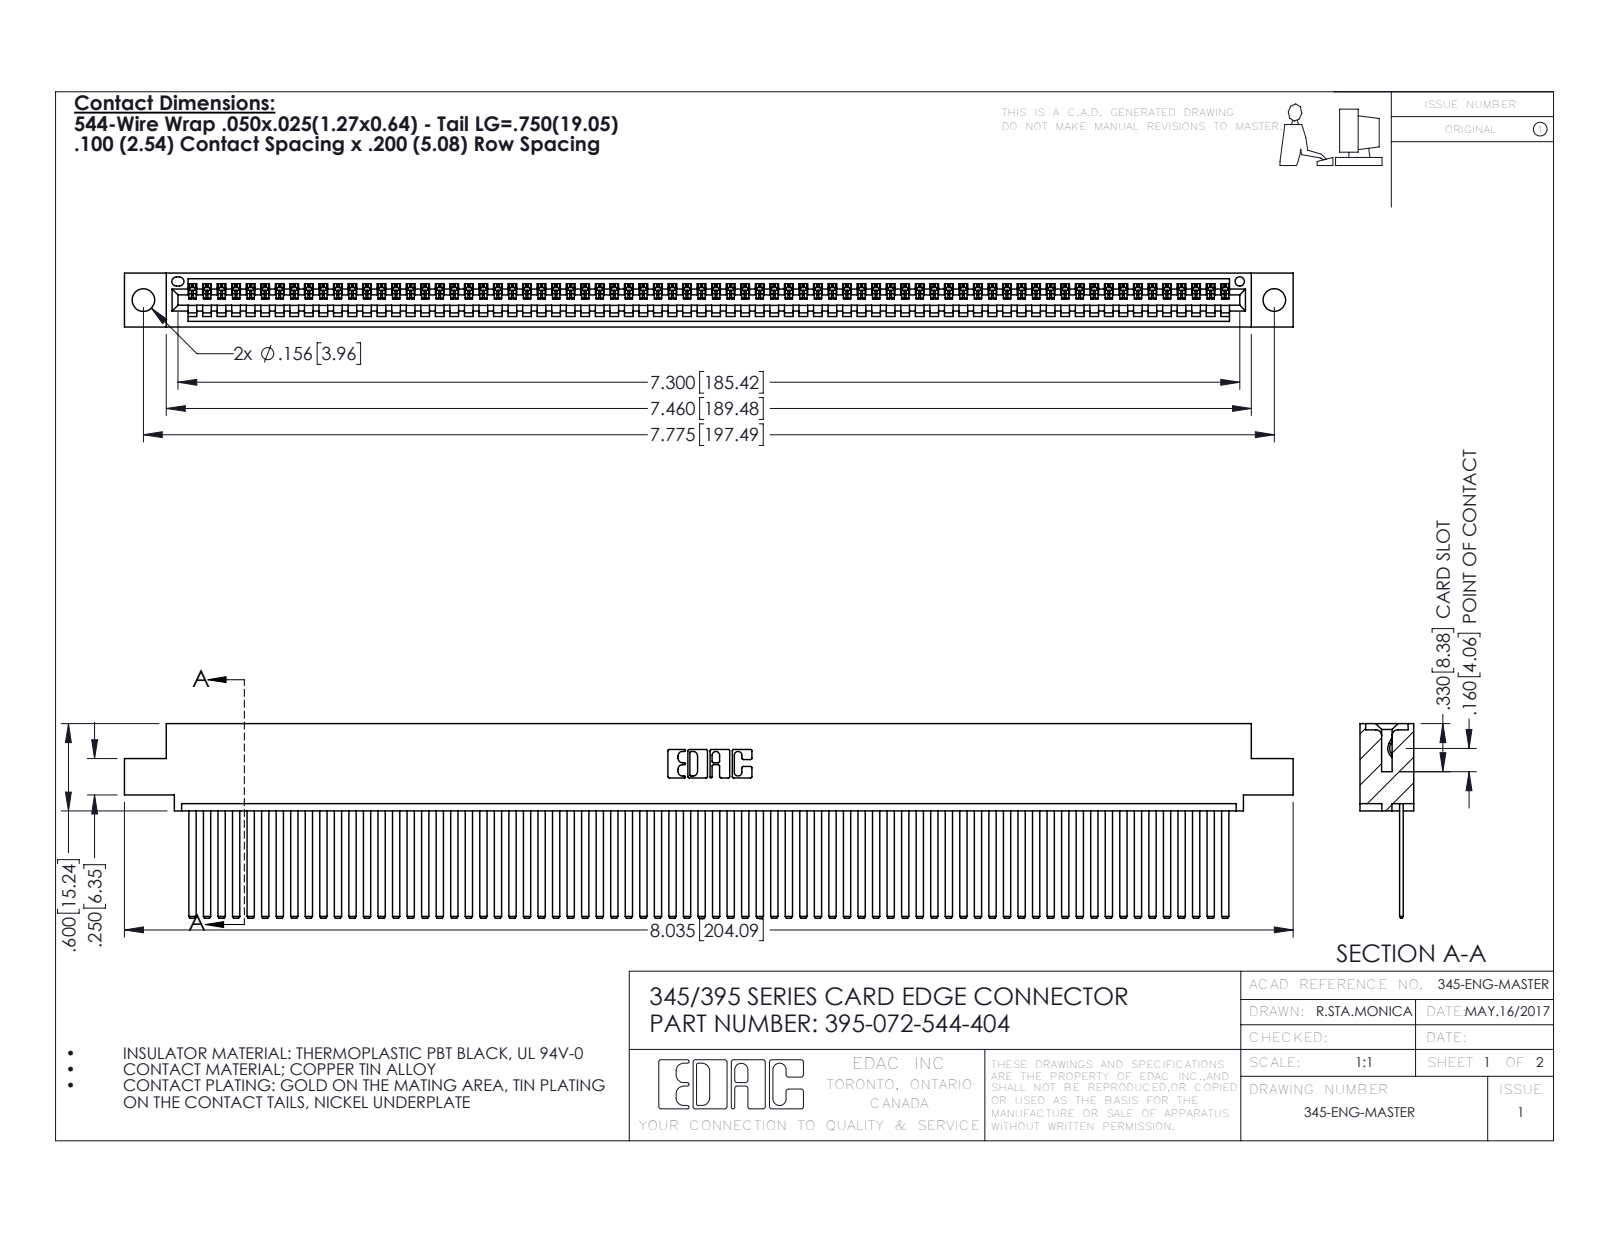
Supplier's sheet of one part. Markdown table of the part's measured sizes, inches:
| quantity | value |
| --- | --- |
| part name | 345 Part_0.110 Offset - 0.156 Dia-TH; 345-292-001_345-293-144; 395-072-544-404 |
| STEP written by | SolidWorks 2016 (CONFIG_CONTROL_DESIGN) |
| units | inches |
| bodies | 73 solids, 3874 faces (2676 planar, 1198 cylindrical, 0 other) |
| overall size | 8.035 × 1.337 × 0.37 |
| volume | 1.239 in³ |
| surface area | 46.16 in² |
| round holes (diameter × count) | 0.156 × 2, 0.064 × 1 |
| partial cylindrical surfaces (radius × count) | 0.006 × 144, 0.01 × 22, 0.007 × 6, 0.031 × 6, 0.026 × 3, 0.031 × 2, 0.04 × 2, 0.014 × 1 |
| main face-to-face distances | 0.072, 0.298, 0.025, 0.098, 0.272, 0.37, 0.2, 0.225, 0.149, 0.072 |
| hole center spacings | 0.27, 7.539, 7.775 |
